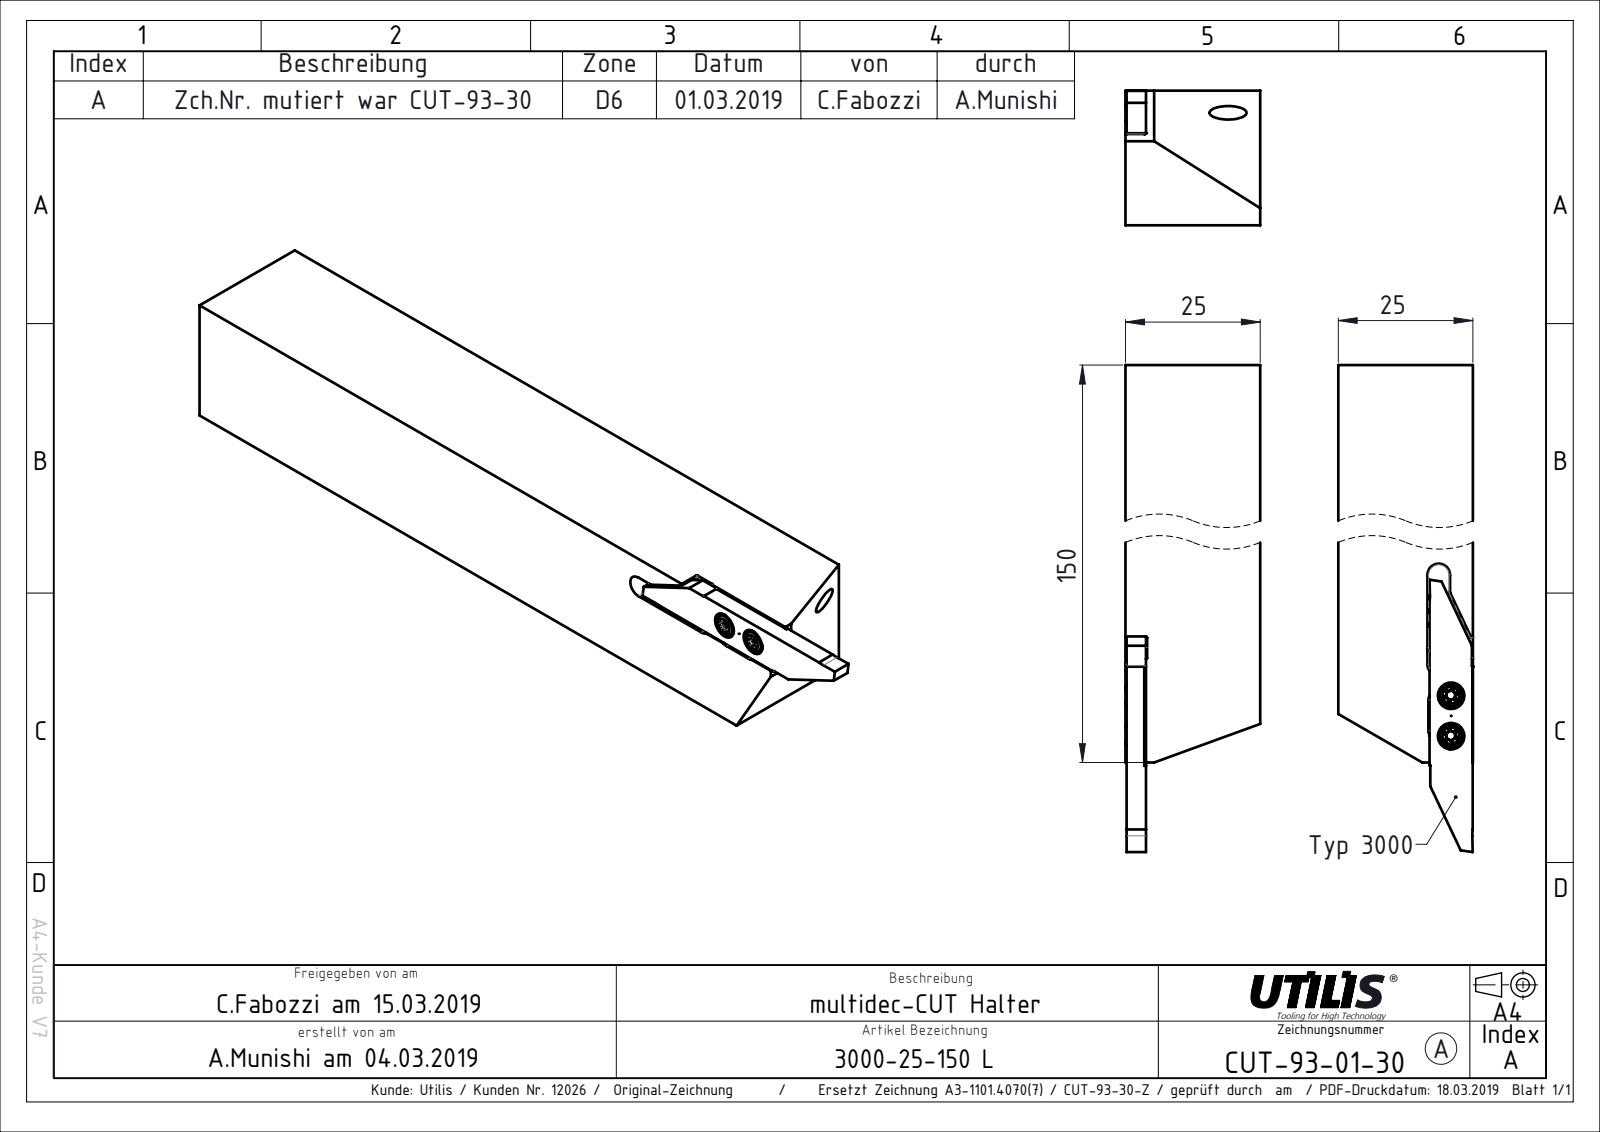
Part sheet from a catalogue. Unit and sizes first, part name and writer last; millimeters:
Units: millimetres
Overall size (bounding box): 166.5 × 25 × 25
Partial cylindrical surfaces — rounded edges, fillets, slot ends (radius × count): R2.1 ×4, R0.15 ×2, R10 ×2
Main face-to-face distances: 25, 24.8, 3.8, 3.6, 21.2, 17, 8, 16.55, 0.45, 8.45
Volume: 91 217 mm³ · Surface area: 16 440 mm²
Bodies: 1 solid, 45 faces (36 planar, 9 cylindrical, 0 other)
Part name (STEP PRODUCT): CUT-93-30
STEP written by: SolidWorks 2016 (AUTOMOTIVE_DESIGN)
